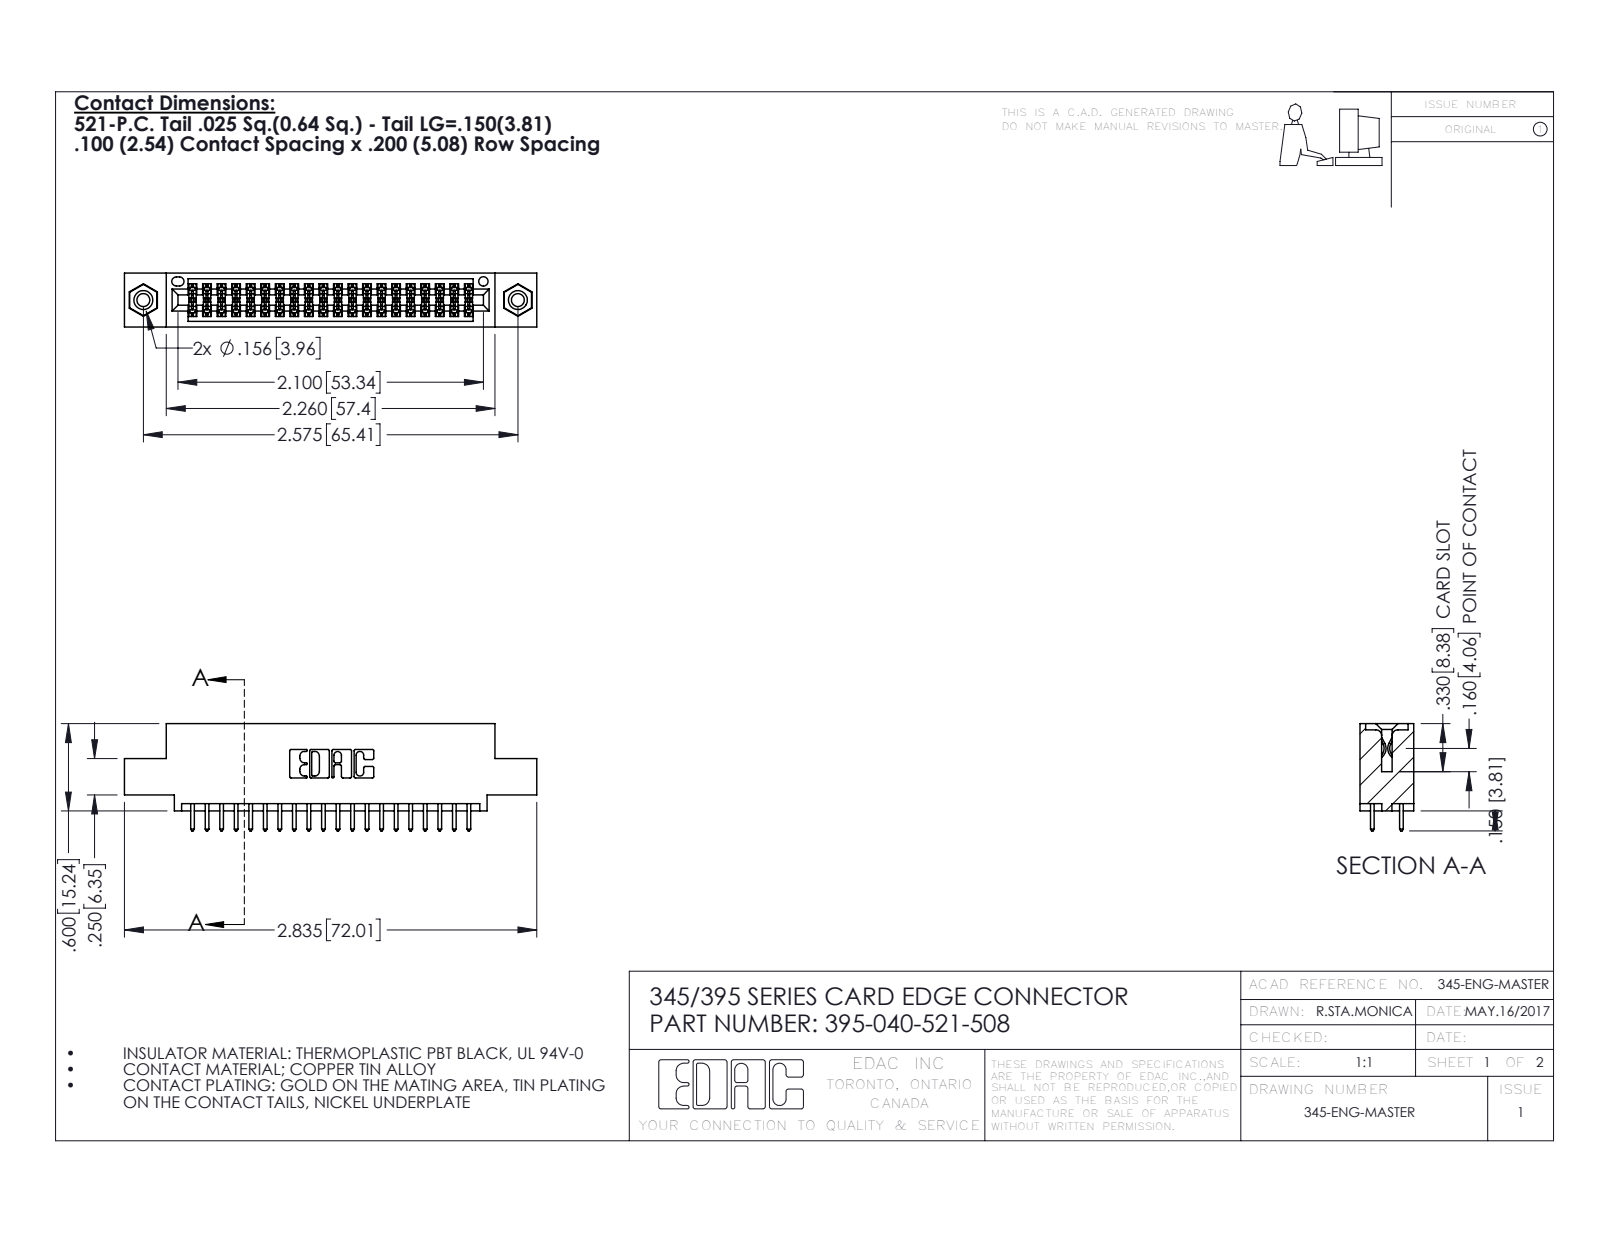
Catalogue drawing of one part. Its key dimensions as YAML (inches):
part_name: "345 Part_0.110 Offset - 0.156 Dia-TI; 395-040-521-508; 345-292-001_345-293-121; 345-250-001_345-250-003-102"
step_written_by: "SolidWorks 2016 (CONFIG_CONTROL_DESIGN)"
units: inches
bodies: {solids: 43, faces: 2190, planar: 1436, cylindrical: 738, other: 16}
overall_size: [2.835, 0.737, 0.37]
volume: 0.409
surface_area: 14.68
round_holes:
  - {diameter: 0.089, count: 2}
  - {diameter: 0.125, count: 2}
  - {diameter: 0.156, count: 2}
  - {diameter: 0.064, count: 1}
round_bosses_or_shafts:
  - {diameter: 0.155, count: 2}
partial_cylinders:
  - {radius: 0.006, count: 60}
  - {radius: 0.01, count: 40}
  - {radius: 0.01, count: 22}
  - {radius: 0.007, count: 6}
  - {radius: 0.031, count: 6}
  - {radius: 0.026, count: 3}
  - {radius: 0.014, count: 2}
  - {radius: 0.019, count: 2}
face_to_face_distances: [0.072, 0.298, 0.2, 0.37, 0.098, 0.272, 0.025, 0.225, 0.175, 0.149]
hole_center_spacings: [0.27, 2.341, 2.575]
